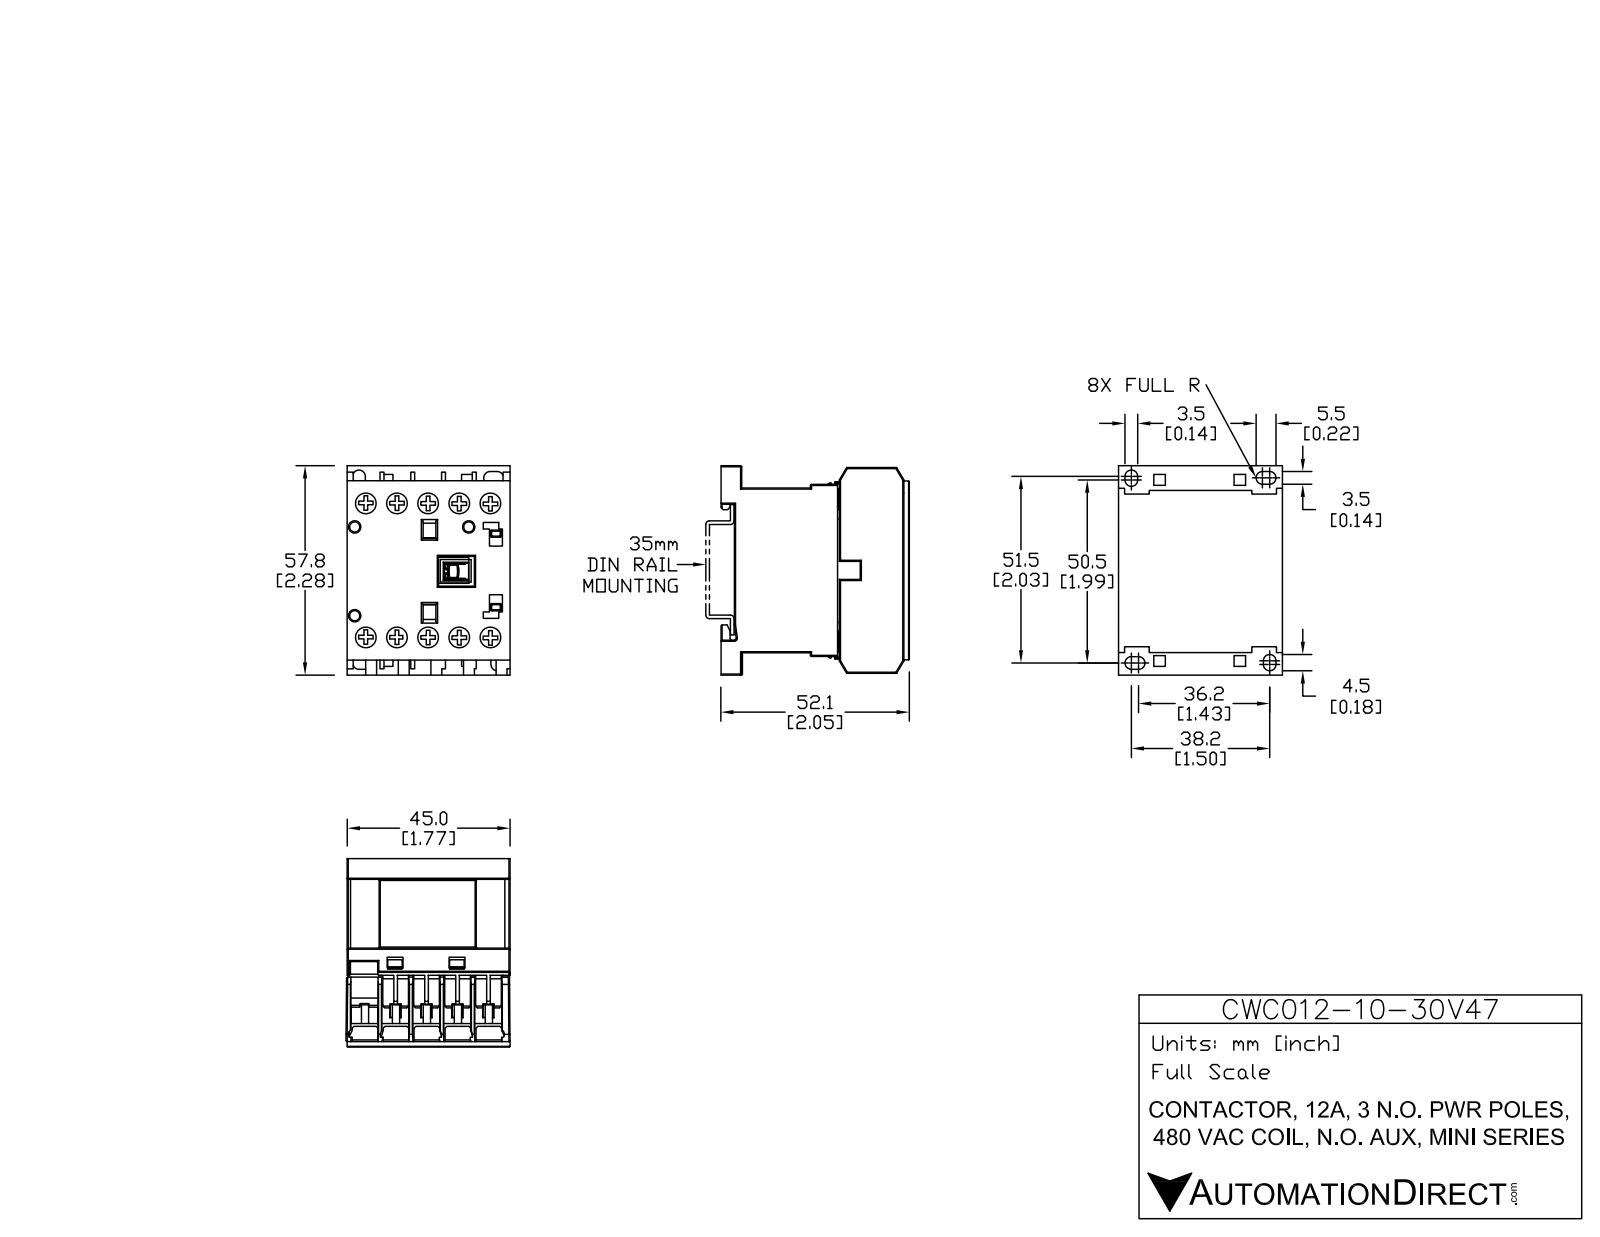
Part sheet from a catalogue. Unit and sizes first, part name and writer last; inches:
Units: inches
Overall size (bounding box): 2.285 × 2.052 × 1.801
Round holes (diameter × count): ⌀0.244 ×10, ⌀0.11 ×3
Round bosses / shafts (diameter × count): ⌀0.232 ×10
Partial cylindrical surfaces — rounded edges, fillets, slot ends (radius × count): R0.012 ×20, R0.068 ×6, R0.068 ×2, R0.013 ×1, R0.017 ×1, R0.022 ×1
Main face-to-face distances: 0.325, 1.791, 0.049, 0.65, 0.374, 0.217, 0.699, 0.202, 0.419, 0.276
Hole centre spacings: 0.337, 1.494, 0.673, 1.603, 1.455, 1.01, 1.771, 0.272
Volume: 5.927 in³ · Surface area: 47.18 in²
Bodies: 15 solids, 535 faces (445 planar, 90 cylindrical, 0 other)
Part name (STEP PRODUCT): CWC12-10-30V47
STEP written by: SolidWorks 2013 (AUTOMOTIVE_DESIGN)
